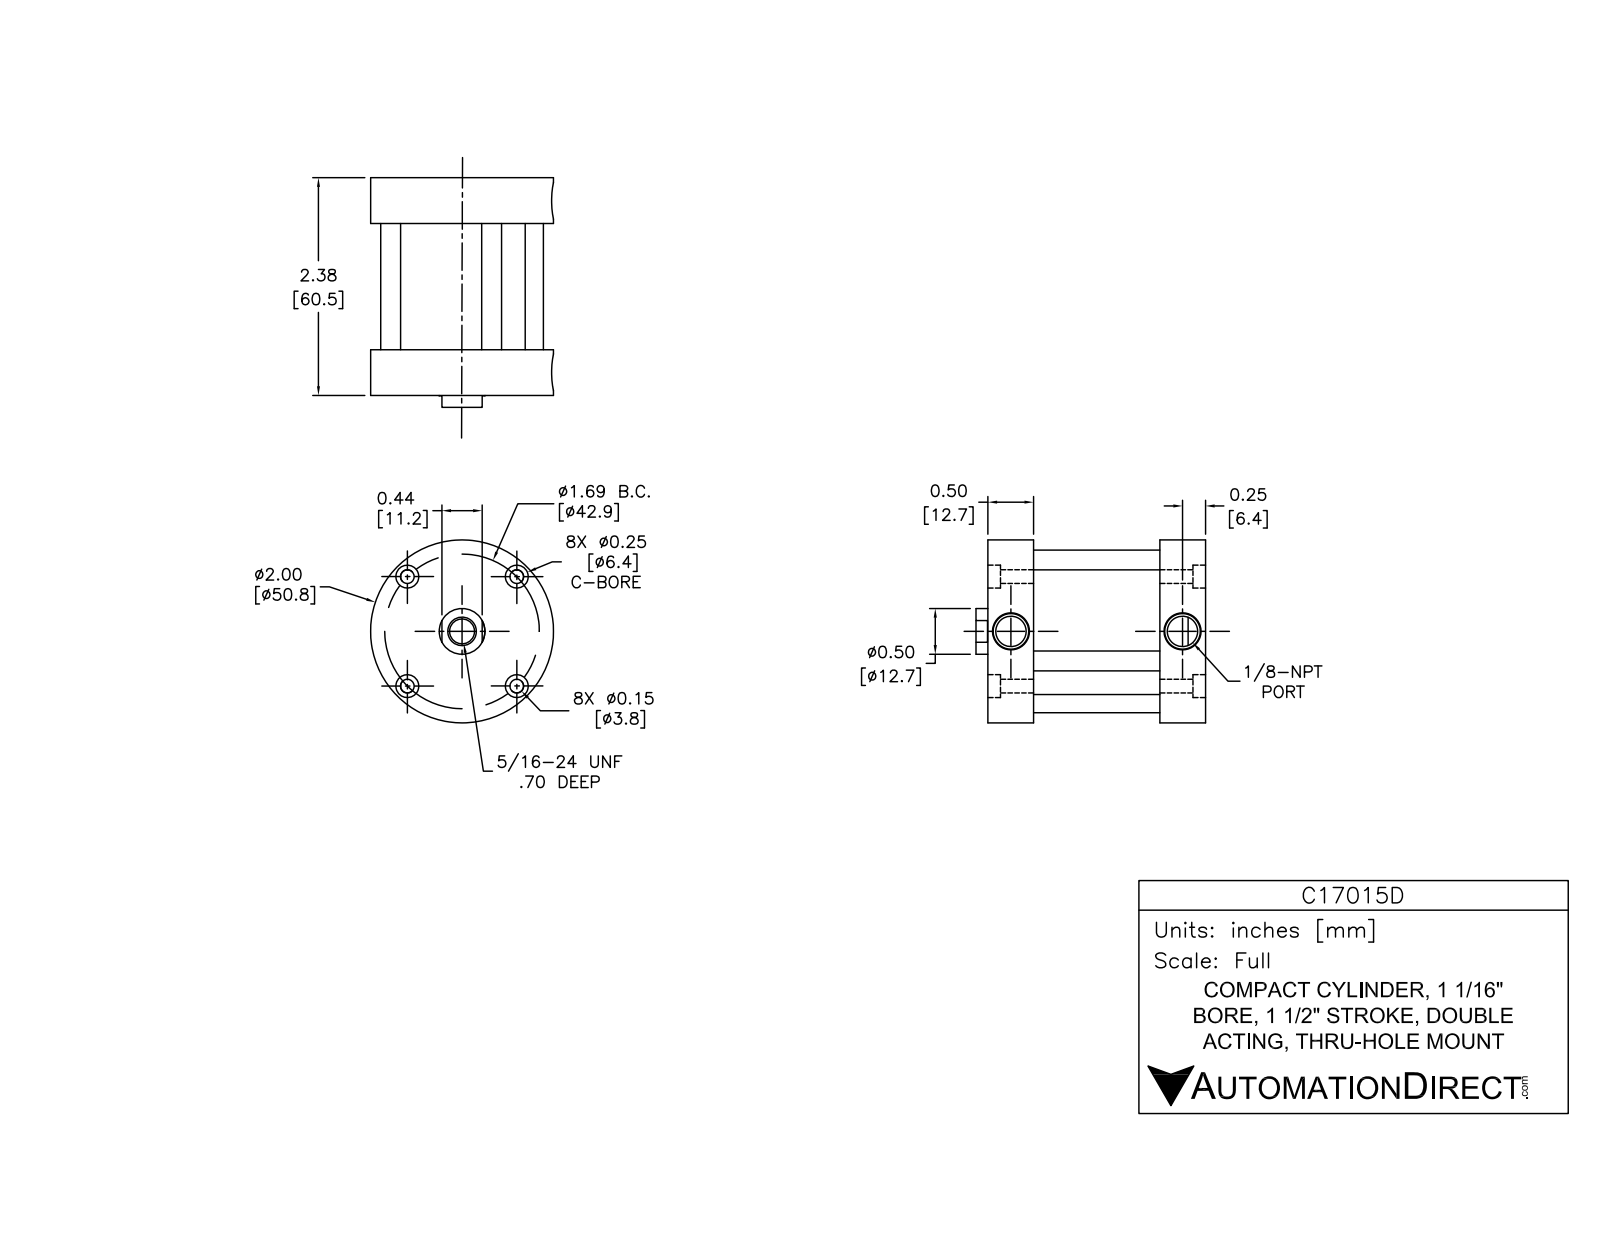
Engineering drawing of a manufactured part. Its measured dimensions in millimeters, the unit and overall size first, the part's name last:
Units: millimetres
Overall size (bounding box): 63.8 × 50.8 × 50.8
Round holes (diameter × count): ⌀3.5 ×4, ⌀4 ×4, ⌀6.4 ×4, ⌀3.2 ×2, ⌀6.8 ×1, ⌀12.7 ×1, ⌀12.8 ×1, ⌀27 ×1, ⌀28.5 ×1
Round bosses / shafts (diameter × count): ⌀6.9 ×4, ⌀50.8 ×1
Main face-to-face distances: 12.7, 47.8, 7.2, 53.3, 5.5, 40.6, 60.5, 35.1, 46.1, 15.2
Hole centre spacings: 8.4, 21.5, 21.5, 23.9, 30.4, 30.4, 35.7, 42.1
Volume: 58 750 mm³ · Surface area: 32 240 mm²
Bodies: 9 solids, 165 faces (49 planar, 98 cylindrical, 18 other)
Part name (STEP PRODUCT): C17015D-FO1_BM_heads (2); C17015D-FO1_BM_rod; C17015D-FO1_BM_r; C17015D-rod_part (+3 more)
STEP written by: SolidWorks 2014 (AUTOMOTIVE_DESIGN)
